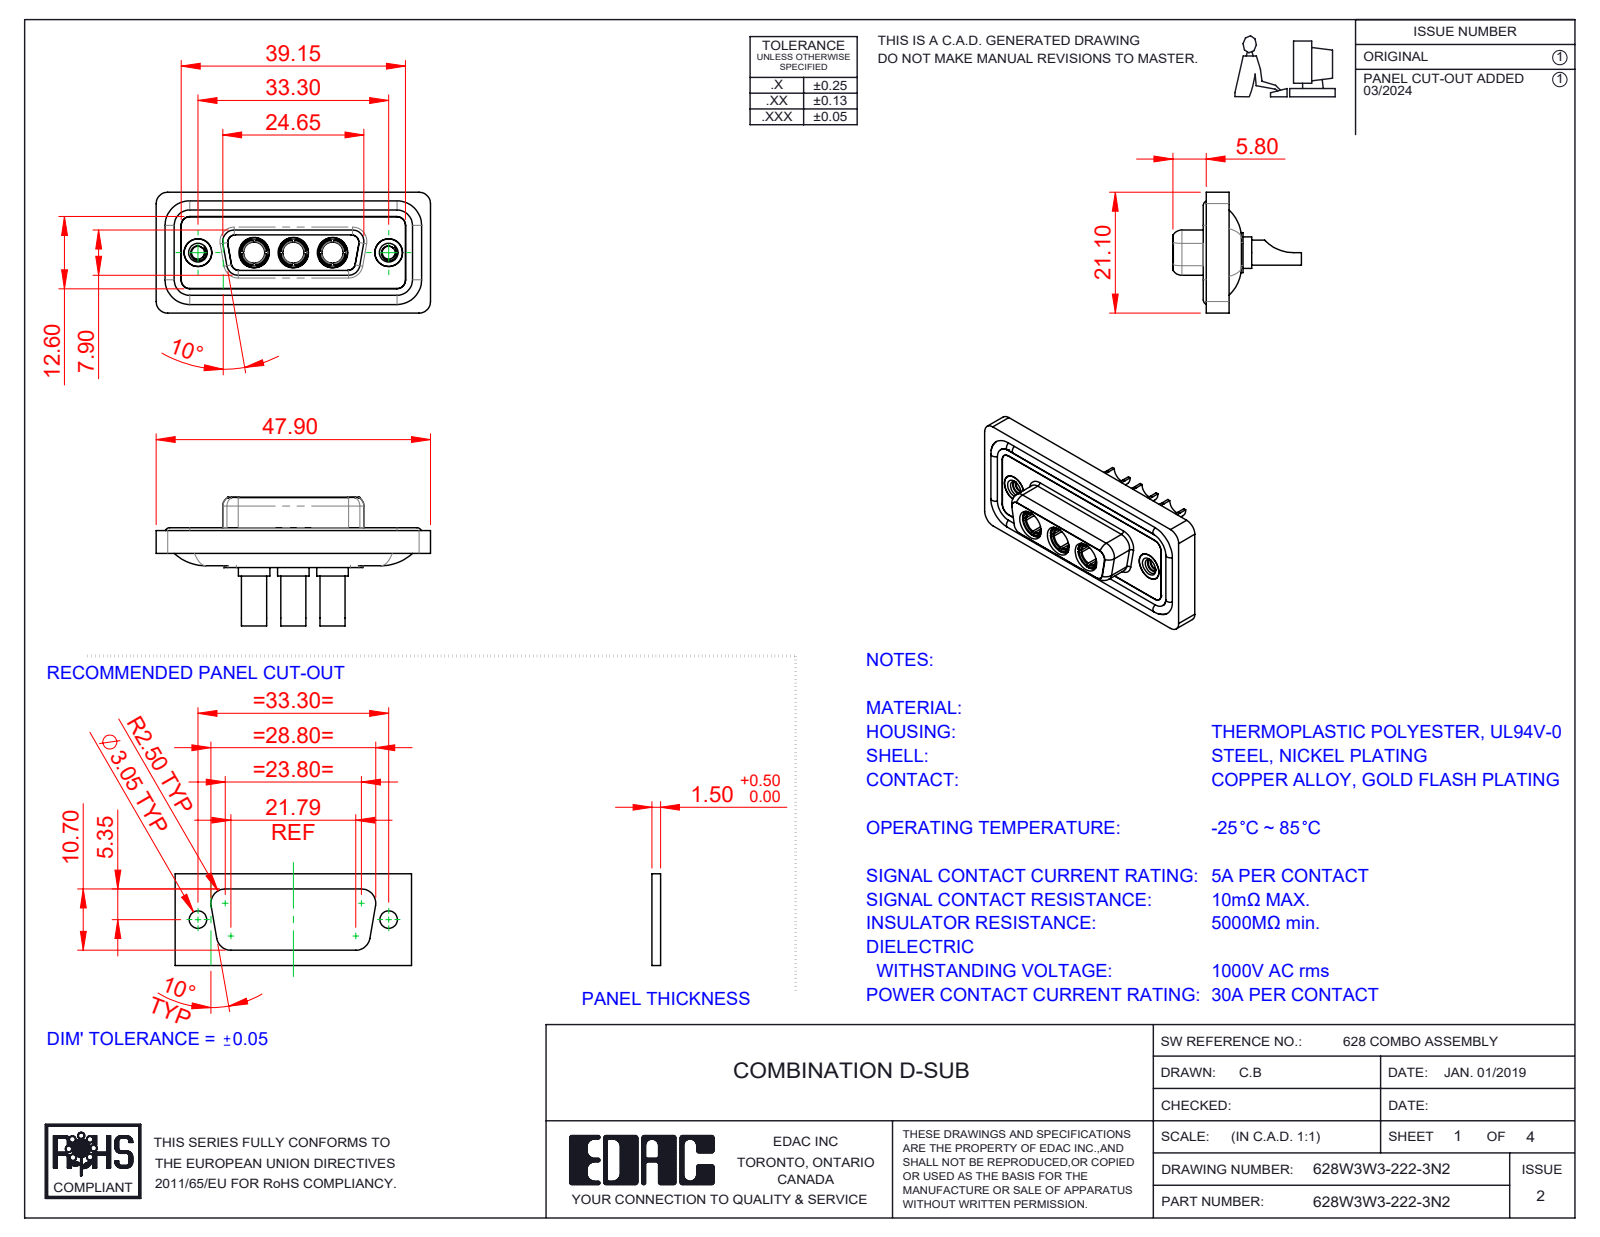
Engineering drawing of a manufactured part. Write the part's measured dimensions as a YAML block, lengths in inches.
part_name: "Power Socket_30A SC; 628Combo Threaded Rivet_2; 628W3W3-222-3N2; 628Combo Shell Rear_15 Contacts (+3 more)"
step_written_by: "SolidWorks 2023 (CONFIG_CONTROL_DESIGN)"
units: inches
bodies: {solids: 13, faces: 626, planar: 201, cylindrical: 266, other: 159}
overall_size: [1.886, 0.884, 0.831]
volume: 0.372
surface_area: 15.59
round_holes:
  - {diameter: 0.191, count: 5}
  - {diameter: 0.138, count: 3}
  - {diameter: 0.146, count: 3}
  - {diameter: 0.209, count: 3}
  - {diameter: 0.089, count: 2}
  - {diameter: 0.157, count: 2}
  - {diameter: 0.159, count: 2}
  - {diameter: 0.197, count: 2}
round_bosses_or_shafts:
  - {diameter: 0.063, count: 4}
  - {diameter: 0.217, count: 3}
  - {diameter: 0.205, count: 3}
  - {diameter: 0.195, count: 3}
  - {diameter: 0.187, count: 3}
  - {diameter: 0.173, count: 3}
  - {diameter: 0.148, count: 3}
  - {diameter: 0.195, count: 2}
partial_cylinders:
  - {radius: 0.059, count: 22}
  - {radius: 0.079, count: 20}
  - {radius: 0.053, count: 12}
  - {radius: 0.063, count: 8}
  - {radius: 0.01, count: 4}
  - {radius: 0.02, count: 4}
  - {radius: 0.024, count: 4}
  - {radius: 0.026, count: 4}
face_to_face_distances: [0.016, 0.071, 0.063, 0.02, 0.293, 0.043, 0.114, 0.222, 0.278, 0.26]
hole_center_spacings: [0.27, 0.386, 0.656, 0.925, 0.539, 1.311]
